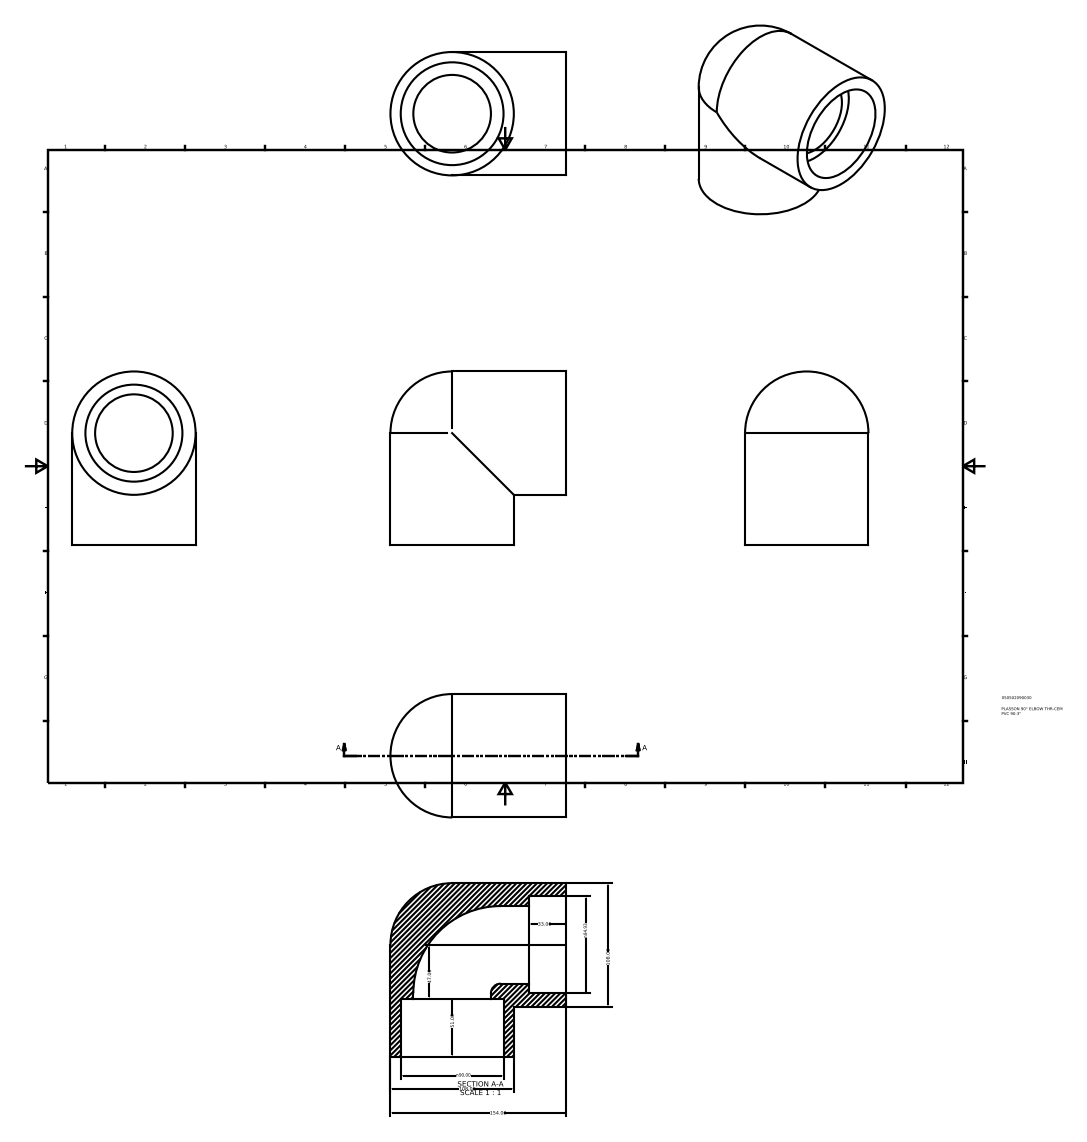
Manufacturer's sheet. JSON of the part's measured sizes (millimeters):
{"part_name": "050502090030", "step_written_by": "Autodesk Inventor 2015 (AUTOMOTIVE_DESIGN)", "units": "millimeters", "bodies": {"solids": 1, "faces": 12, "planar": 4, "cylindrical": 6, "other": 2}, "overall_size": [154, 152, 108], "volume_mm3": 910201, "surface_area_mm2": 119415, "round_holes": [[67.94, 2], [84.93, 1], [90, 1]], "round_bosses_or_shafts": [[108, 2]], "face_to_face_distances": [51, 33]}
